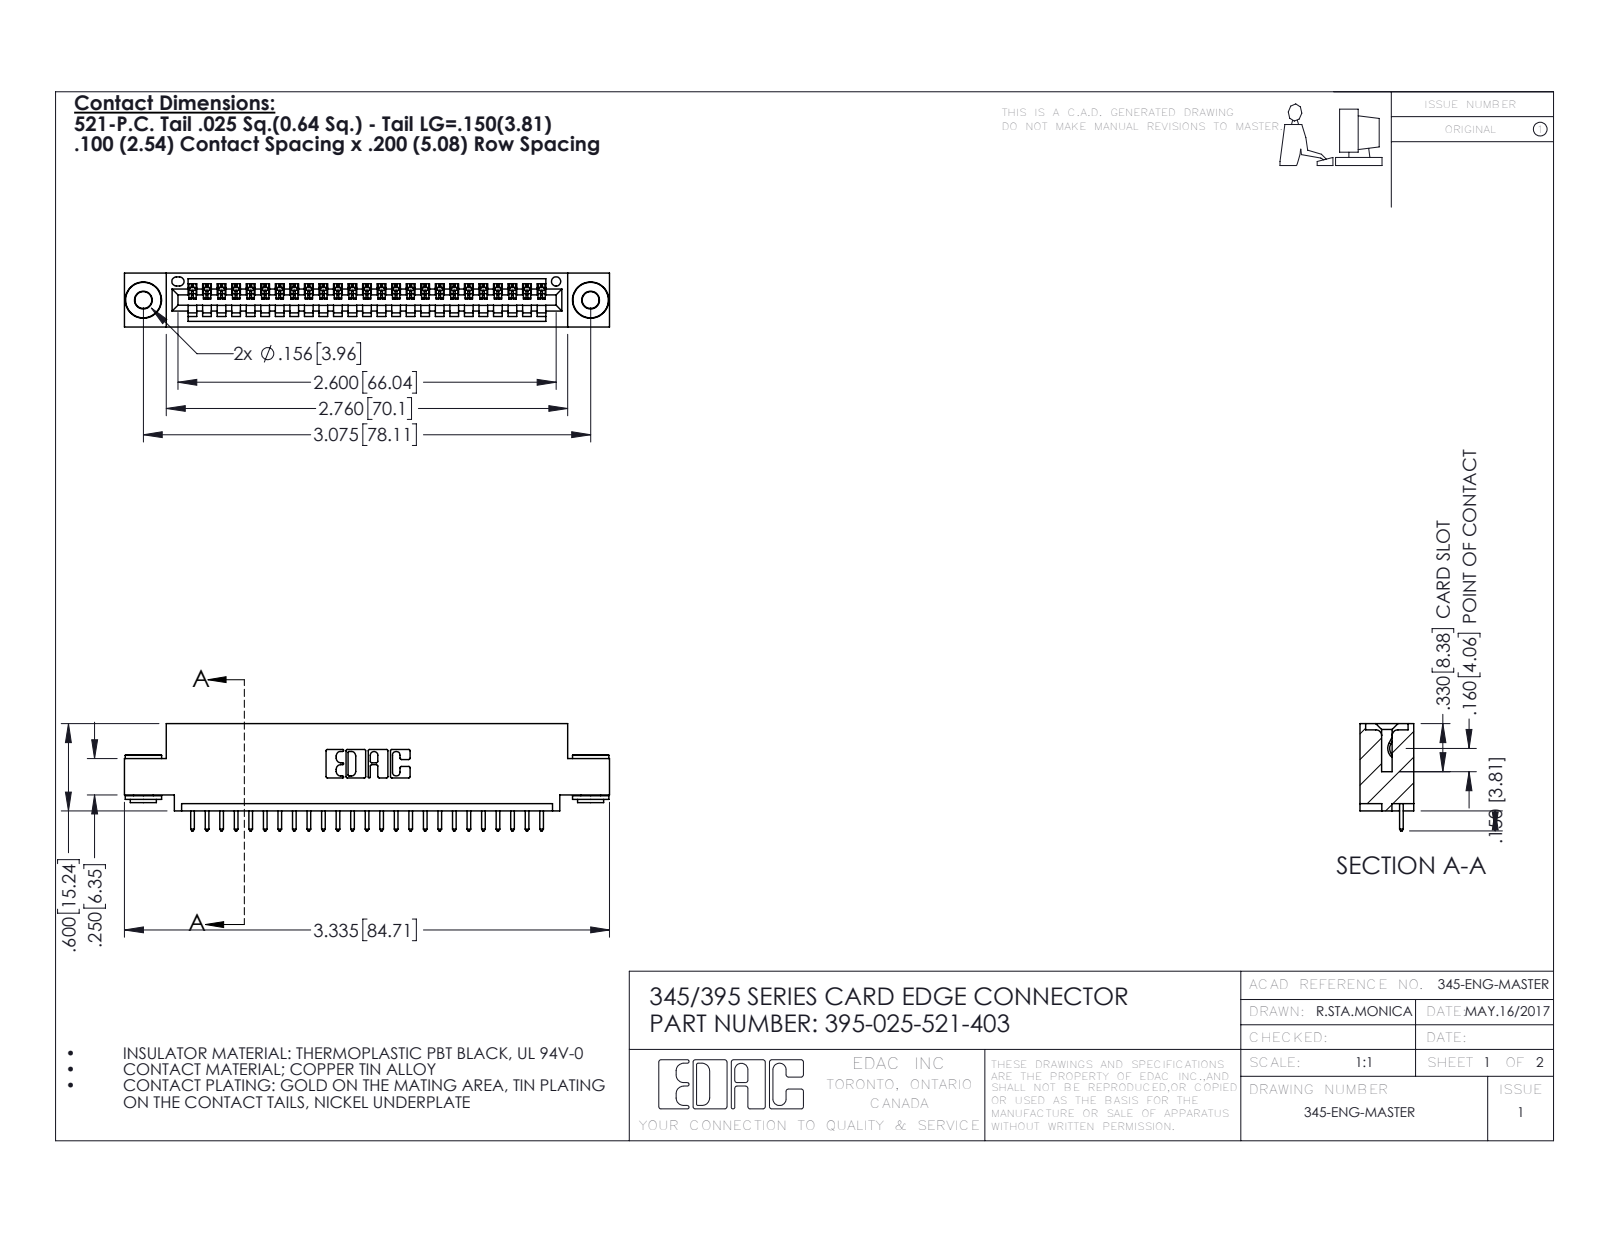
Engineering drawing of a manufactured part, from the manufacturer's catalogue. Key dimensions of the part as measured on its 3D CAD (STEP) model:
Part name (STEP PRODUCT): 345-250-002_345-250-002-102; 395-025-521-403; 345-292-001_345-293-121; 345 Part_0.110 Offset - 0.156 Dia-TH
STEP written by: SolidWorks 2016 (CONFIG_CONTROL_DESIGN)
Units: inches
Bodies: 28 solids, 1618 faces (1094 planar, 516 cylindrical, 8 other)
Overall size (bounding box): 3.335 × 0.737 × 0.37
Volume: 0.475 in³ · Surface area: 15.7 in²
Round holes (diameter × count): ⌀0.116 ×2, ⌀0.156 ×2, ⌀0.064 ×1
Round bosses / shafts (diameter × count): ⌀0.25 ×2, ⌀0.18 ×2, ⌀0.136 ×2
Partial cylindrical surfaces — rounded edges, fillets, slot ends (radius × count): R0.006 ×50, R0.01 ×50, R0.01 ×22, R0.007 ×6, R0.031 ×6, R0.026 ×3, R0.031 ×2, R0.04 ×2
Main face-to-face distances: 0.072, 0.298, 0.37, 0.2, 0.025, 0.098, 0.272, 0.225, 0.149, 0.072
Hole centre spacings: 0.27, 2.84, 3.075
